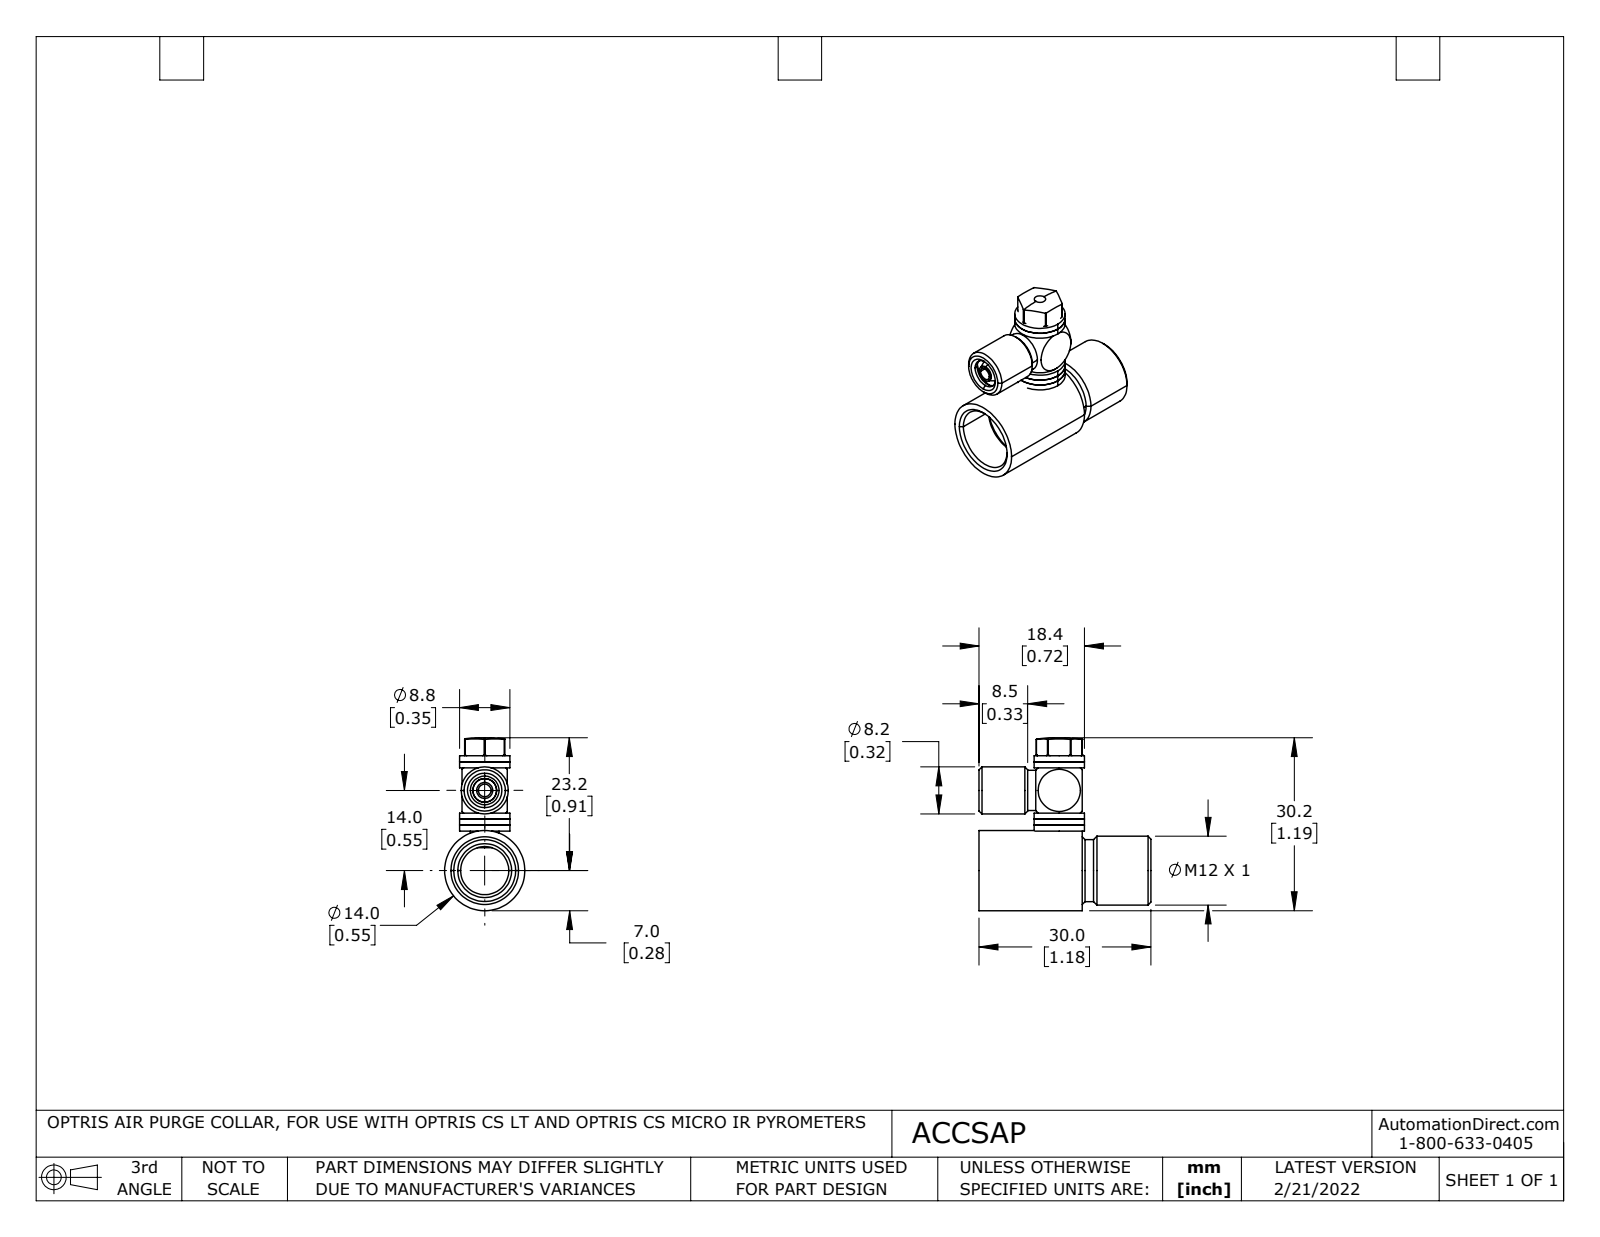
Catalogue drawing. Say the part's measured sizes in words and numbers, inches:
The part is named "ACCSAP - Air purge collar nc fxtb". Its 3-D file was written by "SolidWorks 2021 (AUTOMOTIVE_DESIGN)". It is 7 solids with 151 faces: 33 planar, 65 cylindrical and 53 other. Overall it measures 1.189 by 1.181 by 0.551 inches. Its volume is 0.193 cubic inches and its surface area 6.491 square inches. Round holes: 2 of diameter 0.197, 1 of diameter 0.087, 1 of diameter 0.098, 1 of diameter 0.157, 1 of diameter 0.236, 1 of diameter 0.283, 1 of diameter 0.331, 1 of diameter 0.425, 1 of diameter 0.488. Round bosses or shafts: 1 of diameter 0.551, 1 of diameter 0.472, 1 of diameter 0.346, 1 of diameter 0.323, 1 of diameter 0.276, 1 of diameter 0.138, 1 of diameter 0.11. Partial cylindrical surfaces (rounded edges, fillets, slot ends): 1 of radius 0.157. The main face-to-face distances are 0.041, 0.394, 0.435, 0.083, 0.352, 0.311, 0.476, 0.709, 0.315, 0.124. The hole center spacings are 0.551.
